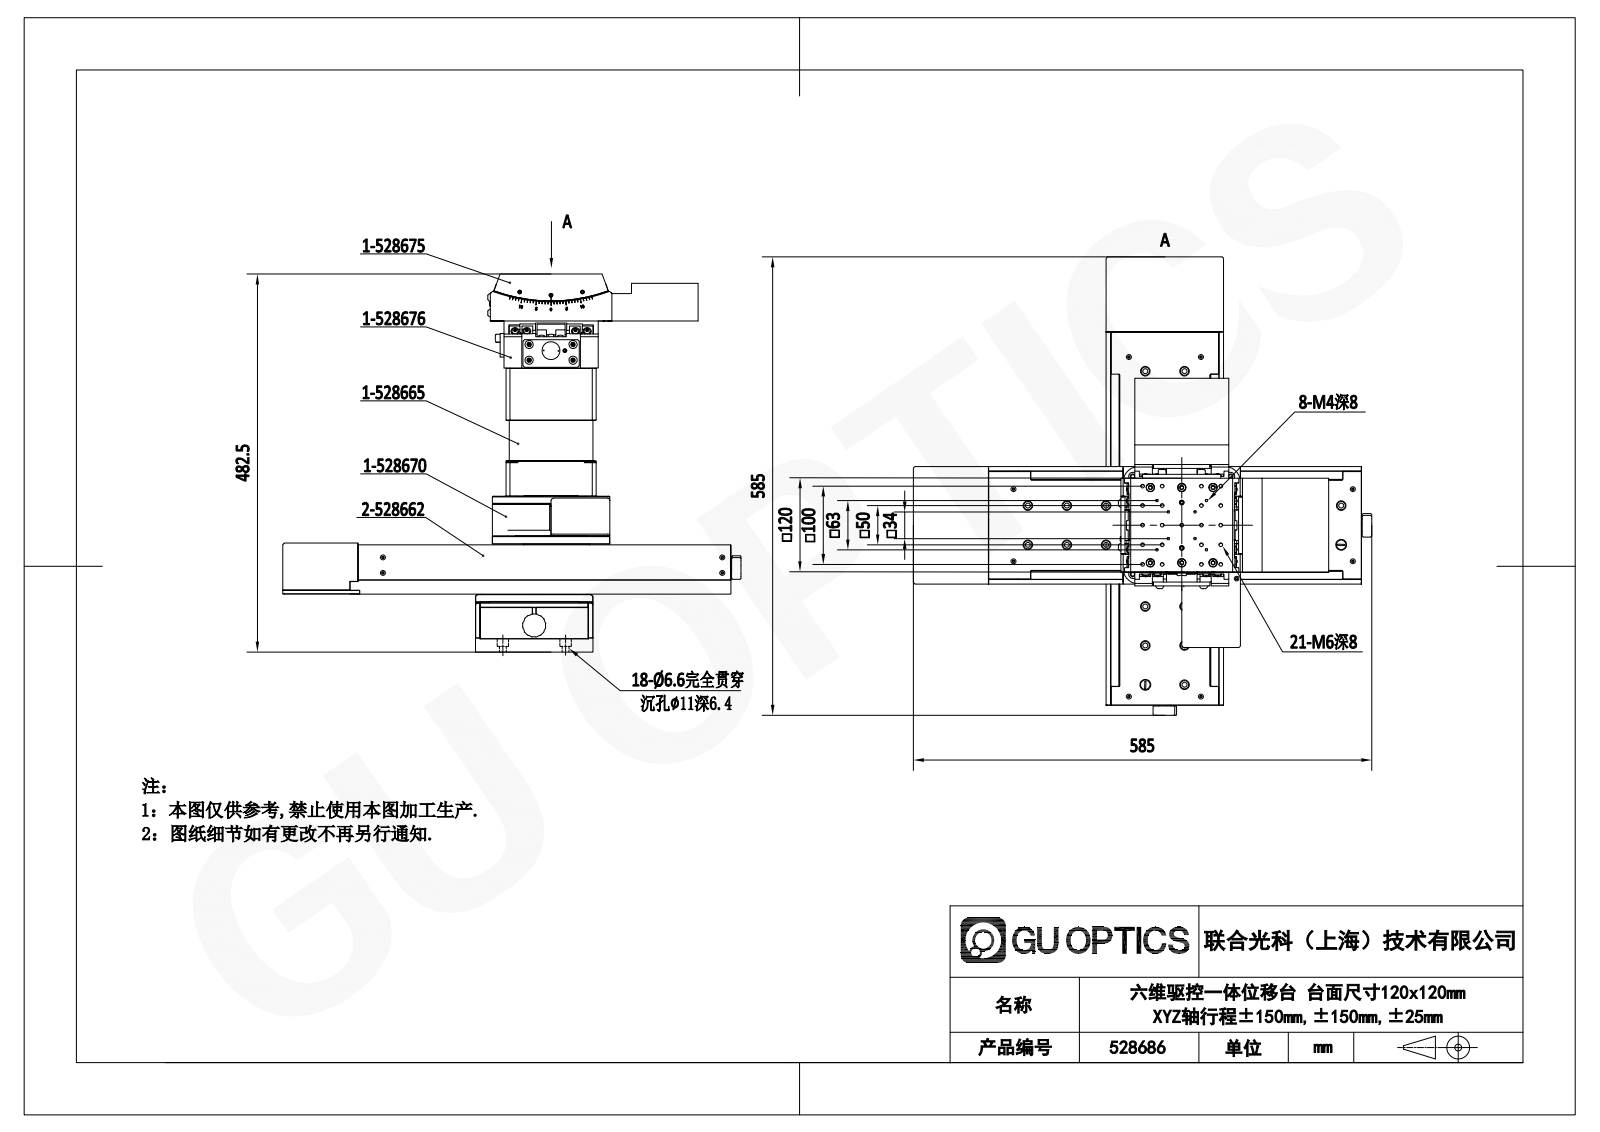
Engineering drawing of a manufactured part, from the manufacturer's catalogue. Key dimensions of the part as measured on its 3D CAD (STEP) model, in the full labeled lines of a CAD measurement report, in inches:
Part name (STEP PRODUCT): 528686; 528675; 528665; 528662 (+2 more)
STEP written by: SolidWorks 2020 (CONFIG_CONTROL_DESIGN)
Units: inches
Bodies: 263 solids, 10600 faces (6561 planar, 2304 cylindrical, 1735 other)
Overall size (bounding box): 23.031 × 23.031 × 18.996
Volume: 609 in³ · Surface area: 4 303 in²
Round holes (diameter × count): ⌀0.197 ×175, ⌀0.13 ×107, ⌀0.134 ×82, ⌀0.098 ×80, ⌀0.433 ×75, ⌀0.256 ×73, ⌀0.26 ×59, ⌀0.315 ×48, ⌀0.492 ×36, ⌀0.097 ×32, ⌀0.138 ×32, ⌀0.236 ×29
Round bosses / shafts (diameter × count): ⌀0.157 ×44, ⌀0.236 ×35, ⌀0.394 ×32, ⌀0.276 ×24, ⌀0.374 ×8, ⌀0.335 ×8, ⌀0.098 ×8, ⌀0.197 ×7
Partial cylindrical surfaces — rounded edges, fillets, slot ends (radius × count): R0.197 ×93, R0.079 ×59, R0.039 ×45, R0.012 ×36, R0.138 ×20, R0.118 ×19, R0.295 ×18, R0.157 ×10
Main face-to-face distances: 2.913, 0.236, 2.244, 2.48, 1.772, 0.709, 1.535, 0.669, 5.669, 0.098
Hole centre spacings: 0.492, 2.461, 0.984, 1.476, 1.969, 1.1, 1.556, 2.029
